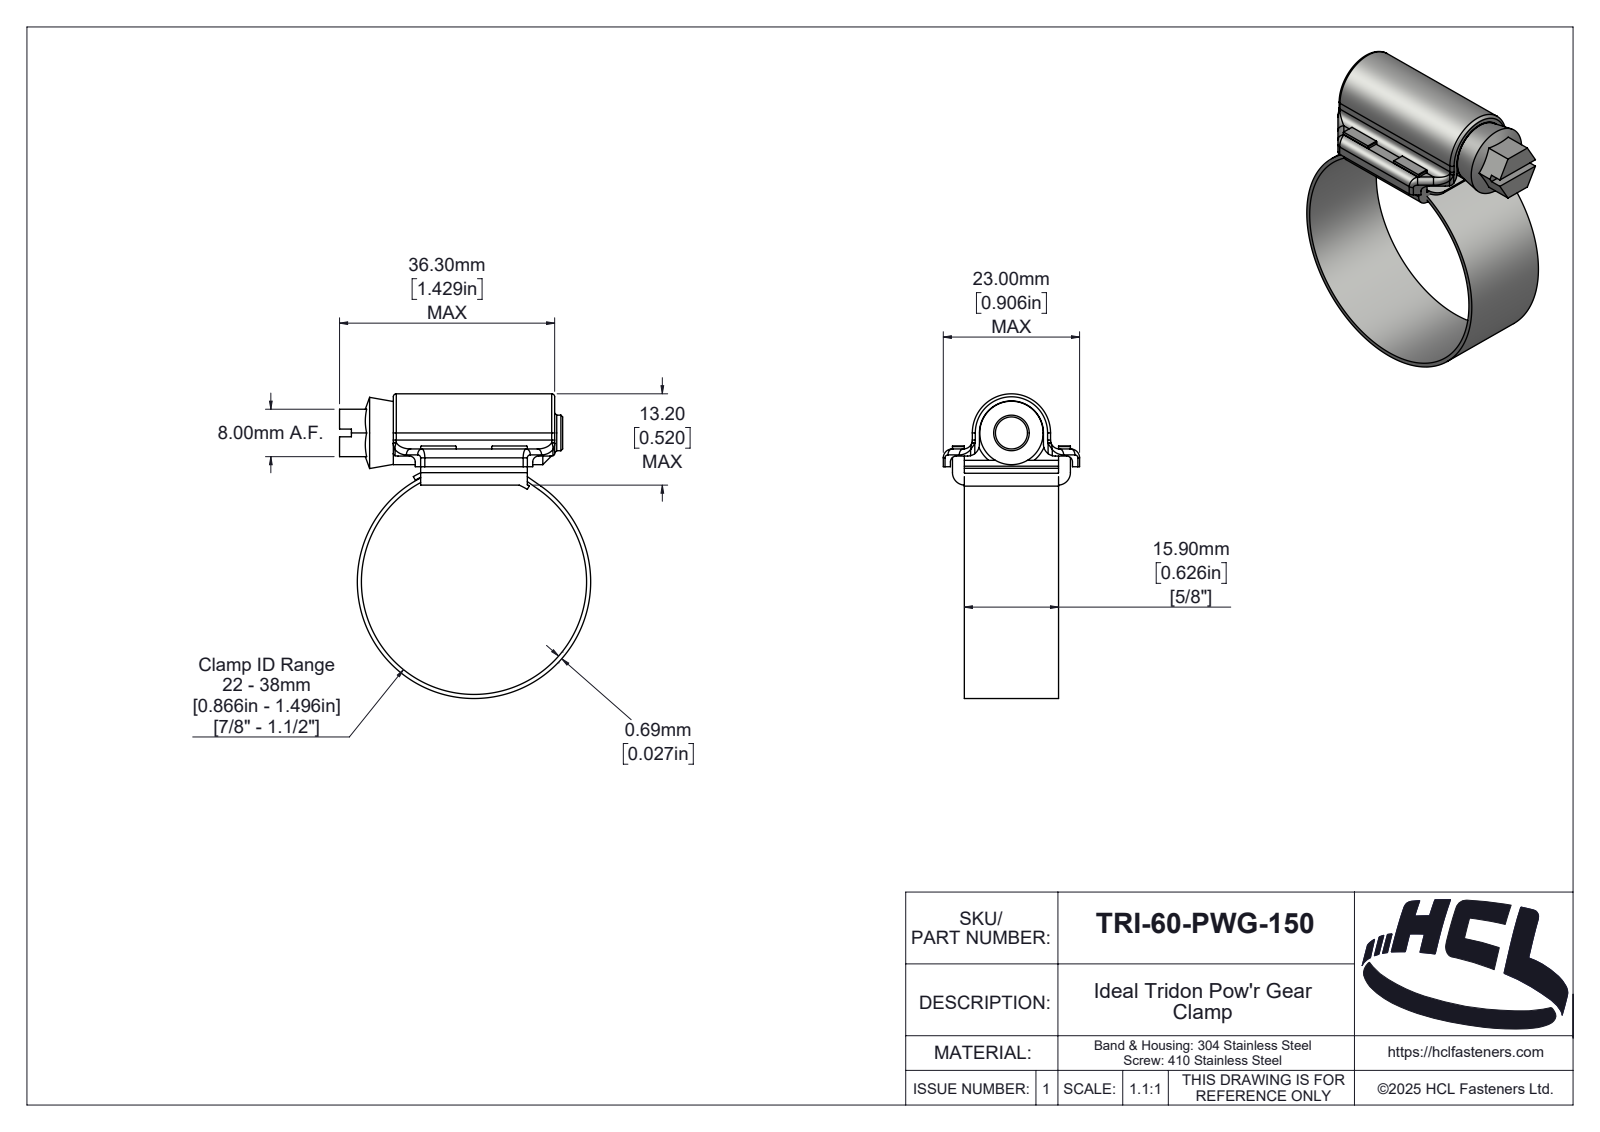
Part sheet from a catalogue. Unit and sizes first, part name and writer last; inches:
Units: inches
Overall size (bounding box): 2.023 × 1.669 × 0.906
Round holes (diameter × count): ⌀1.496 ×1
Round bosses / shafts (diameter × count): ⌀1.55 ×1, ⌀0.421 ×1, ⌀0.236 ×1
Partial cylindrical surfaces — rounded edges, fillets, slot ends (radius × count): R0.039 ×14, R0.02 ×4, R0.059 ×4, R0.079 ×3, R0.004 ×2, R0.083 ×2, R0.118 ×2, R0.106 ×1
Main face-to-face distances: 0.079, 0.626, 0.705, 0.193, 0.047, 0.179, 0.132, 0.604, 0.1, 0.526
Volume: 0.412 in³ · Surface area: 14.44 in²
Bodies: 4 solids, 167 faces (85 planar, 52 cylindrical, 30 other)
Part name (STEP PRODUCT): TRI-60-PWG
STEP written by: SolidWorks 2025 (CONFIG_CONTROL_DESIGN)
